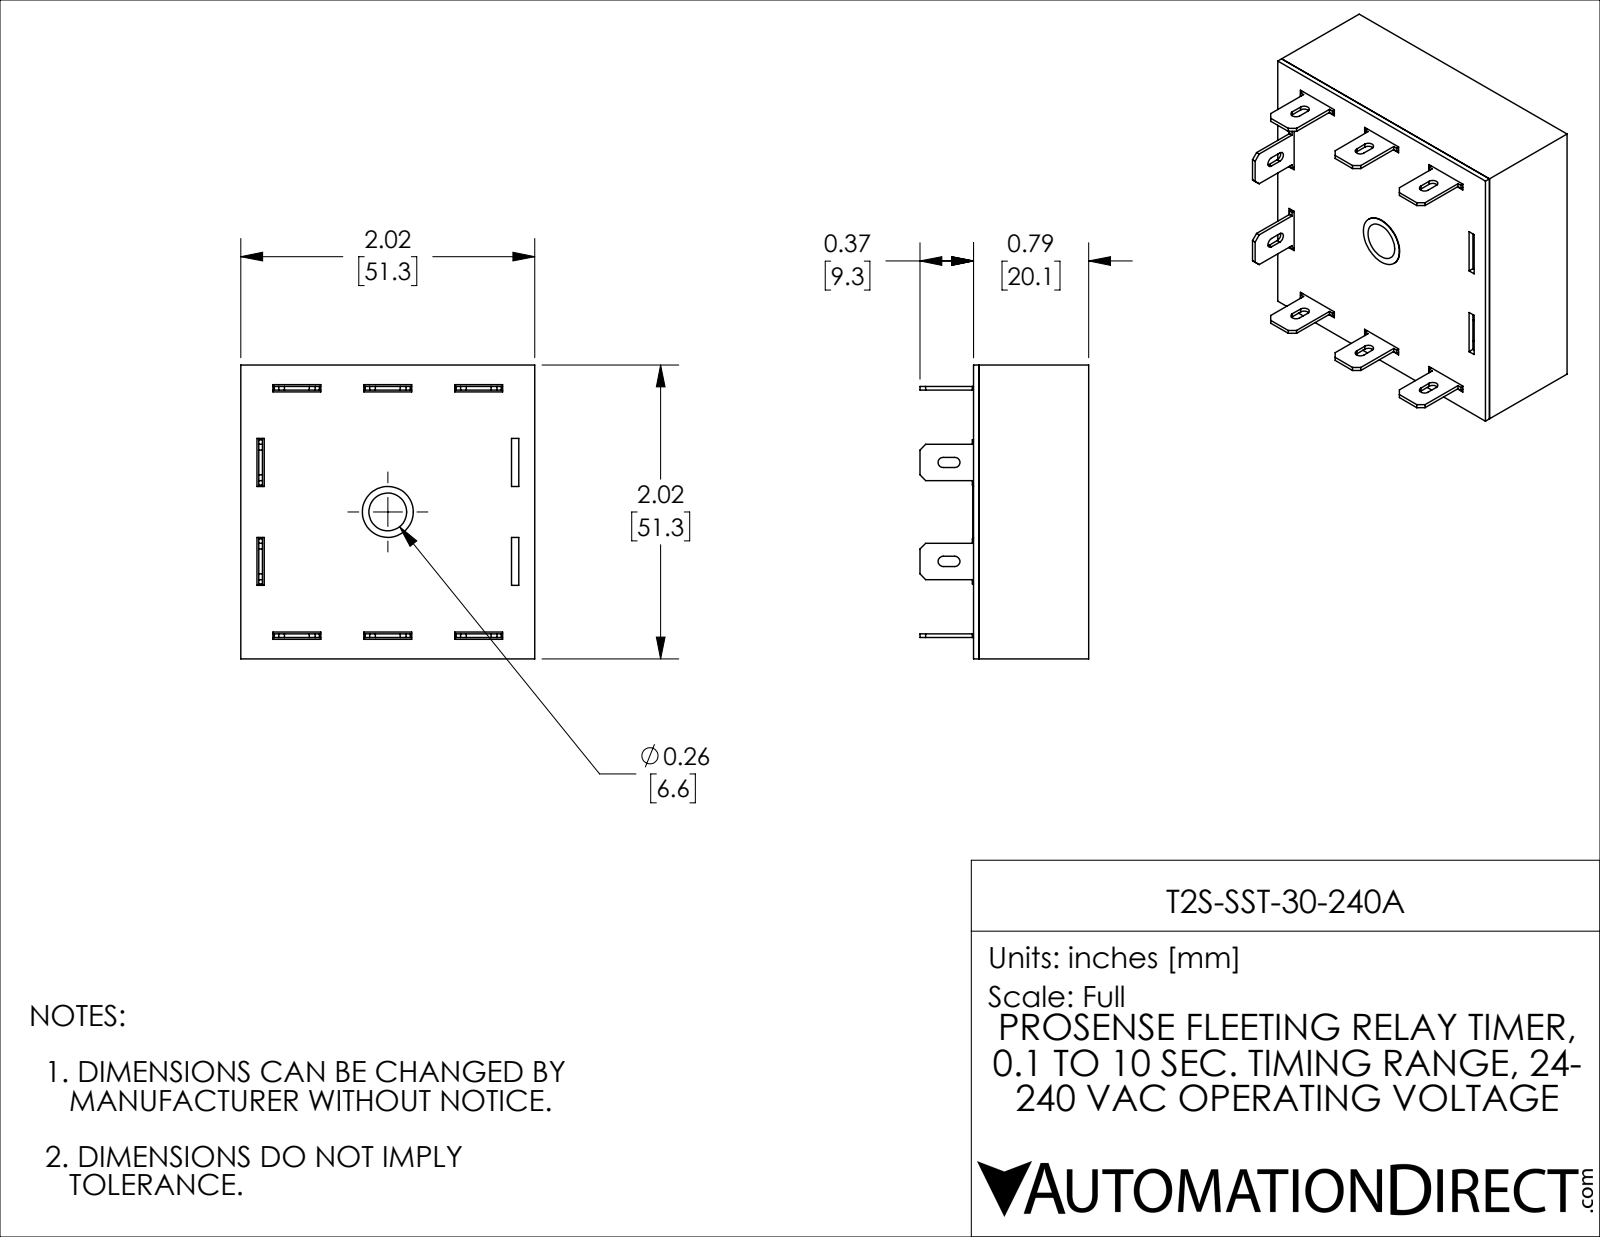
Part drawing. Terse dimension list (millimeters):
name: T2S-SST-30-240A
written by: SolidWorks 2021 (CONFIG_CONTROL_DESIGN)
unit: mm
bodies: 10 solids, 256 faces (234 planar, 20 cylindrical, 2 other)
size: 51.31 × 51.31 × 29.46
volume: 11 042 mm³; area: 22 819 mm²
holes: 1× ⌀8.89
rounds: 10× R0.89
face distances: 1.14, 50.16, 19.15, 20.12, 0.97, 18.01, 18.98, 51.3, 49.02, 3.74
